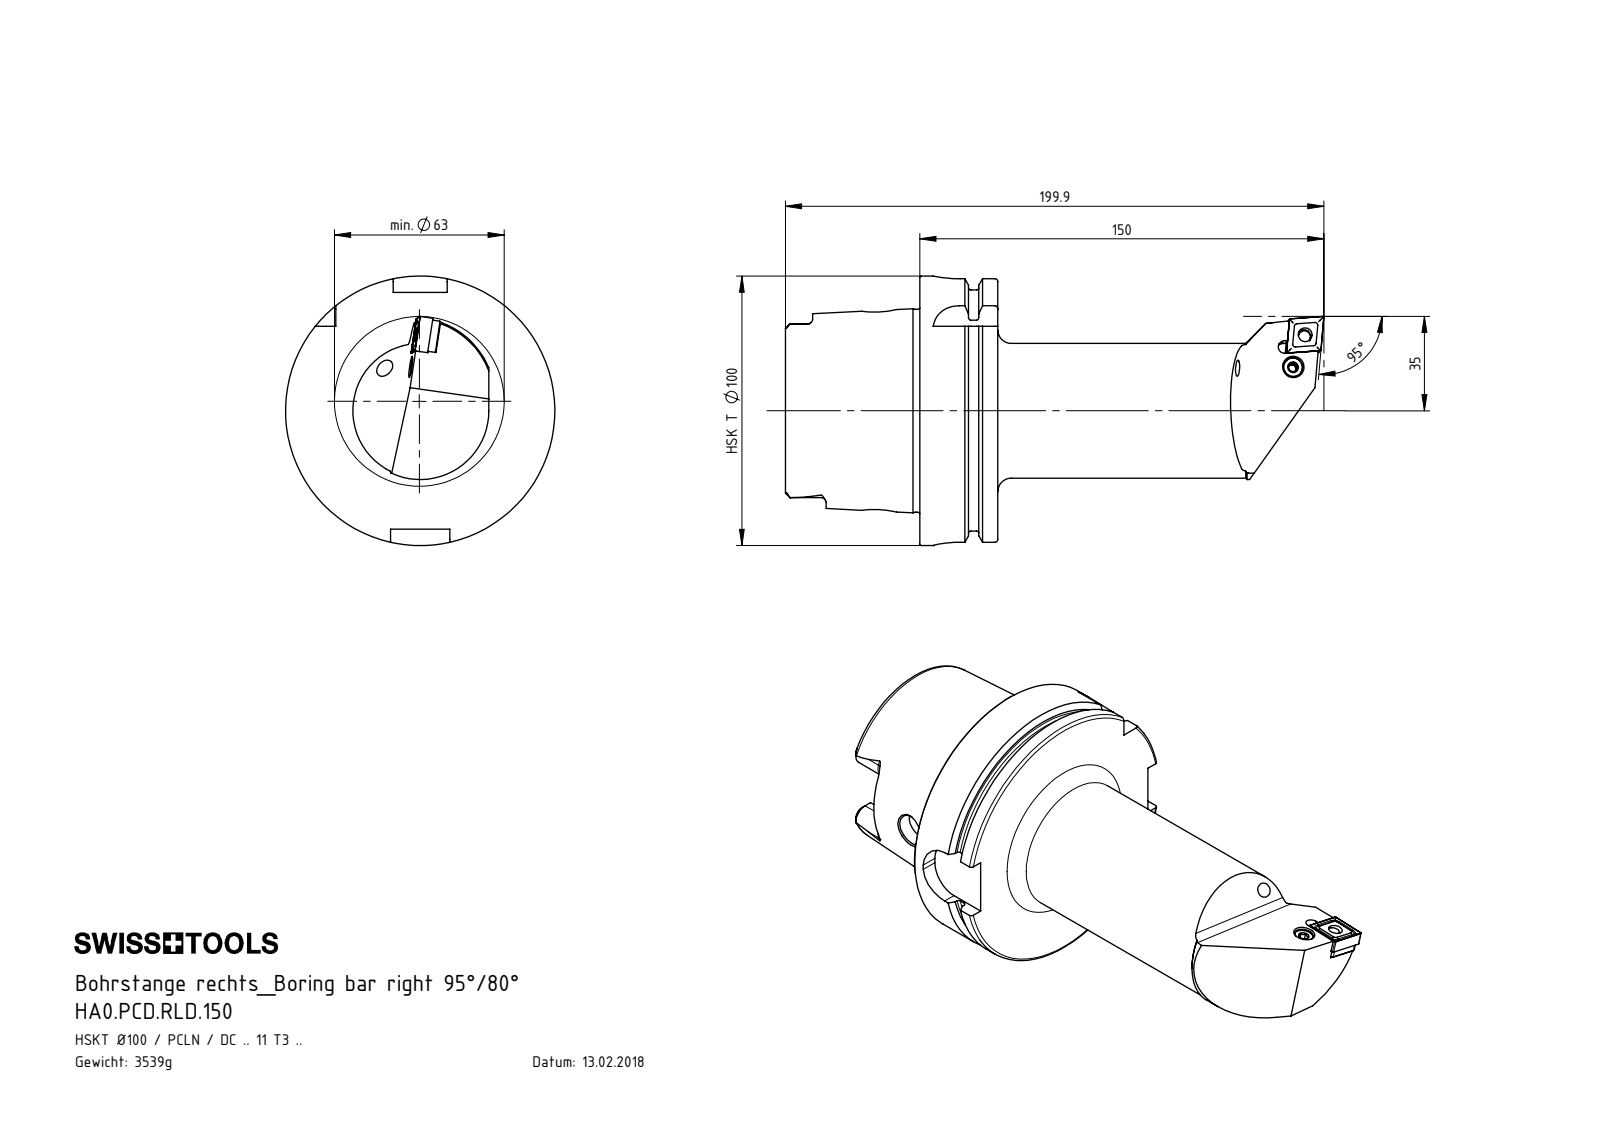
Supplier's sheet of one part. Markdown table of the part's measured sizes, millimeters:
| quantity | value |
| --- | --- |
| part name | HA0-PCD.RLD.150; WCD-ER3.101.000_A; WCD-ER4.101.017_A; KVT_MB_600_060 (+3 more) |
| STEP written by | SolidWorks 2012 (CONFIG_CONTROL_DESIGN) |
| units | millimeters |
| bodies | 7 solids, 366 faces (112 planar, 105 cylindrical, 149 other) |
| overall size | 199.9 × 100 × 100 |
| volume | 448 477 mm³ |
| surface area | 73 494 mm² |
| round holes (diameter × count) | 5 × 3, 12 × 2, 5.16 × 1, 6 × 1, 6.4 × 1, 7 × 1, 8.4 × 1, 10 × 1, 22.5 × 1, 26 × 1, 53 × 1, 63 × 1 |
| round bosses / shafts (diameter × count) | 100 × 1, 91.95 × 1, 75.26 × 1, 50 × 1, 8 × 1, 7.9 × 1, 6.4 × 1, 6 × 1 |
| partial cylindrical surfaces (radius × count) | 1.9 × 6, 0.4 × 4, 1 × 4, 10 × 4, 2.5 × 2, 4.83 × 2, 4.88 × 2, 2.1 × 1 |
| main face-to-face distances | 28.95, 12.45, 16.5, 49.9, 62.35, 78.85, 87.8, 78.2, 28.3, 15.85 |
| hole center spacings | 12.81, 12.87 |
